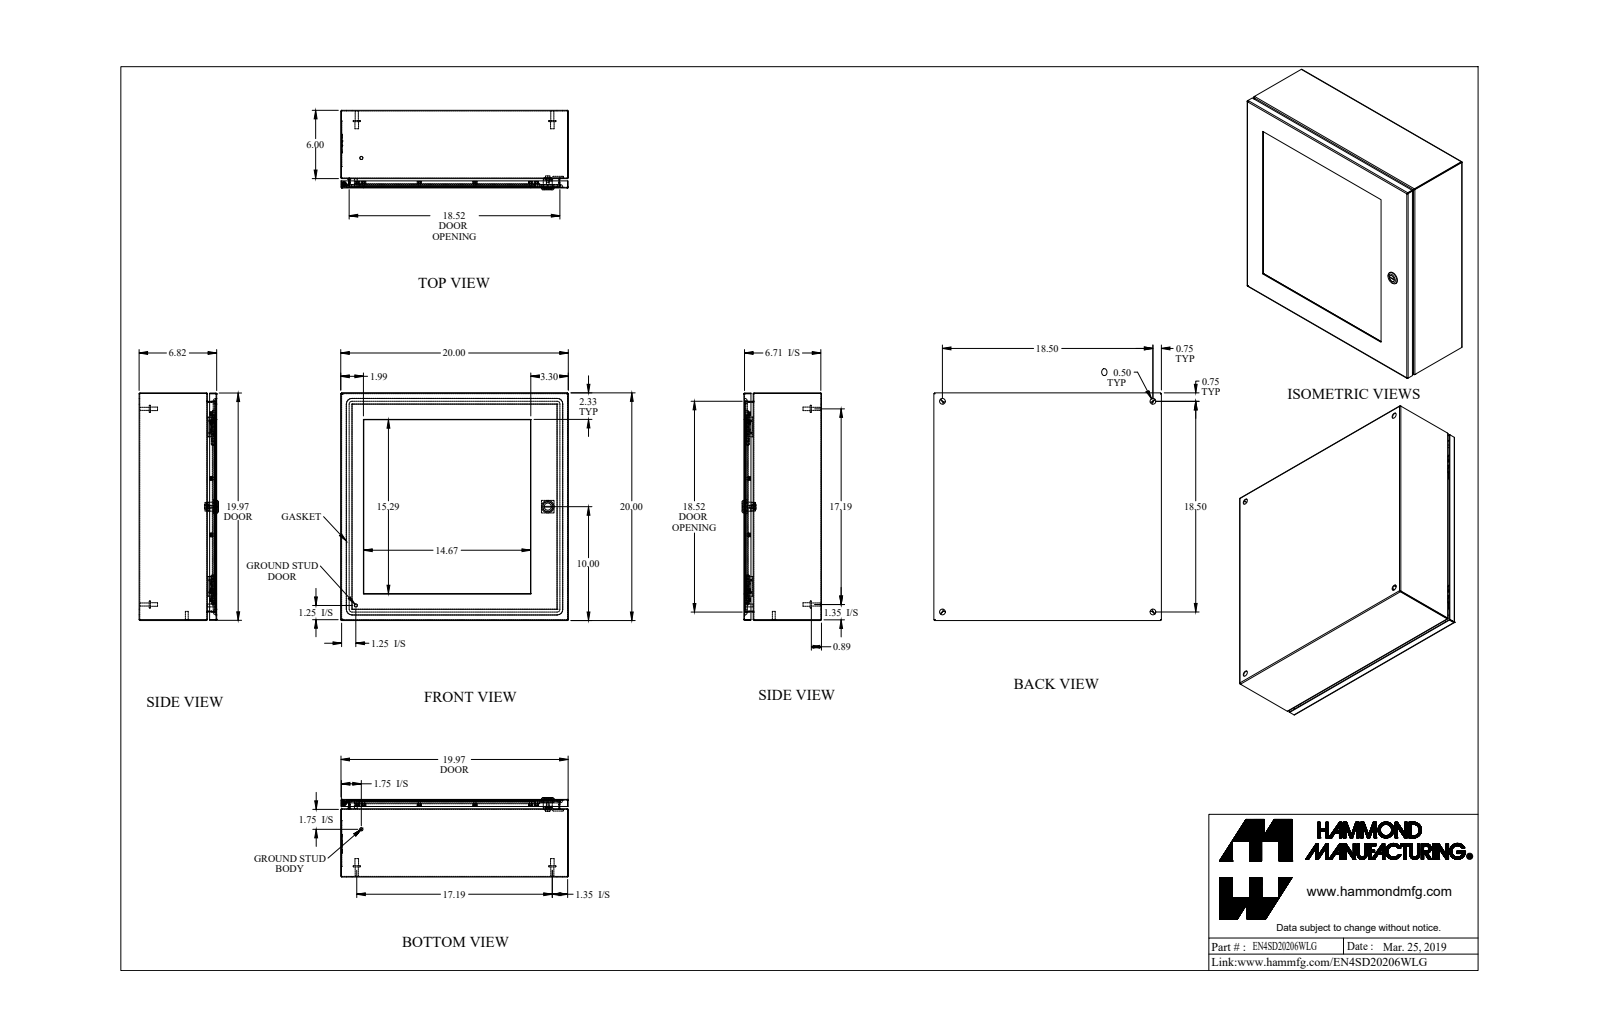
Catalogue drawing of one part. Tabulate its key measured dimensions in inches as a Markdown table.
| quantity | value |
| --- | --- |
| part name | EN4SD20206WLG_Default |
| STEP written by | SolidWorks 2019 (CONFIG_CONTROL_DESIGN) |
| units | inches |
| bodies | 62 solids, 1265 faces (628 planar, 389 cylindrical, 248 other) |
| overall size | 20 × 20 × 6.982 |
| volume | 142.9 in³ |
| surface area | 3 300 in² |
| round holes (diameter × count) | 0.13 × 16, 0.25 × 16, 0.5 × 4, 0.172 × 1, 0.232 × 1, 0.24 × 1, 0.242 × 1, 0.625 × 1, 0.785 × 1 |
| round bosses / shafts (diameter × count) | 0.226 × 17, 0.368 × 16, 0.164 × 16, 0.625 × 4, 0.313 × 4, 0.27 × 4, 0.281 × 2, 0.25 × 2 |
| partial cylindrical surfaces (radius × count) | 0.029 × 21, 0.086 × 21, 0.25 × 16, 0.125 × 10, 19 × 8, 0.006 × 4, 0.016 × 4, 0.062 × 4 |
| main face-to-face distances | 0.057, 6.765, 19.943, 6.708, 0.25, 6.458, 6.515, 19.886, 20, 0.307 |
| hole center spacings | 9.78, 16.333, 4.889, 4.89, 4.89, 4.891, 10.324, 16.471 |
